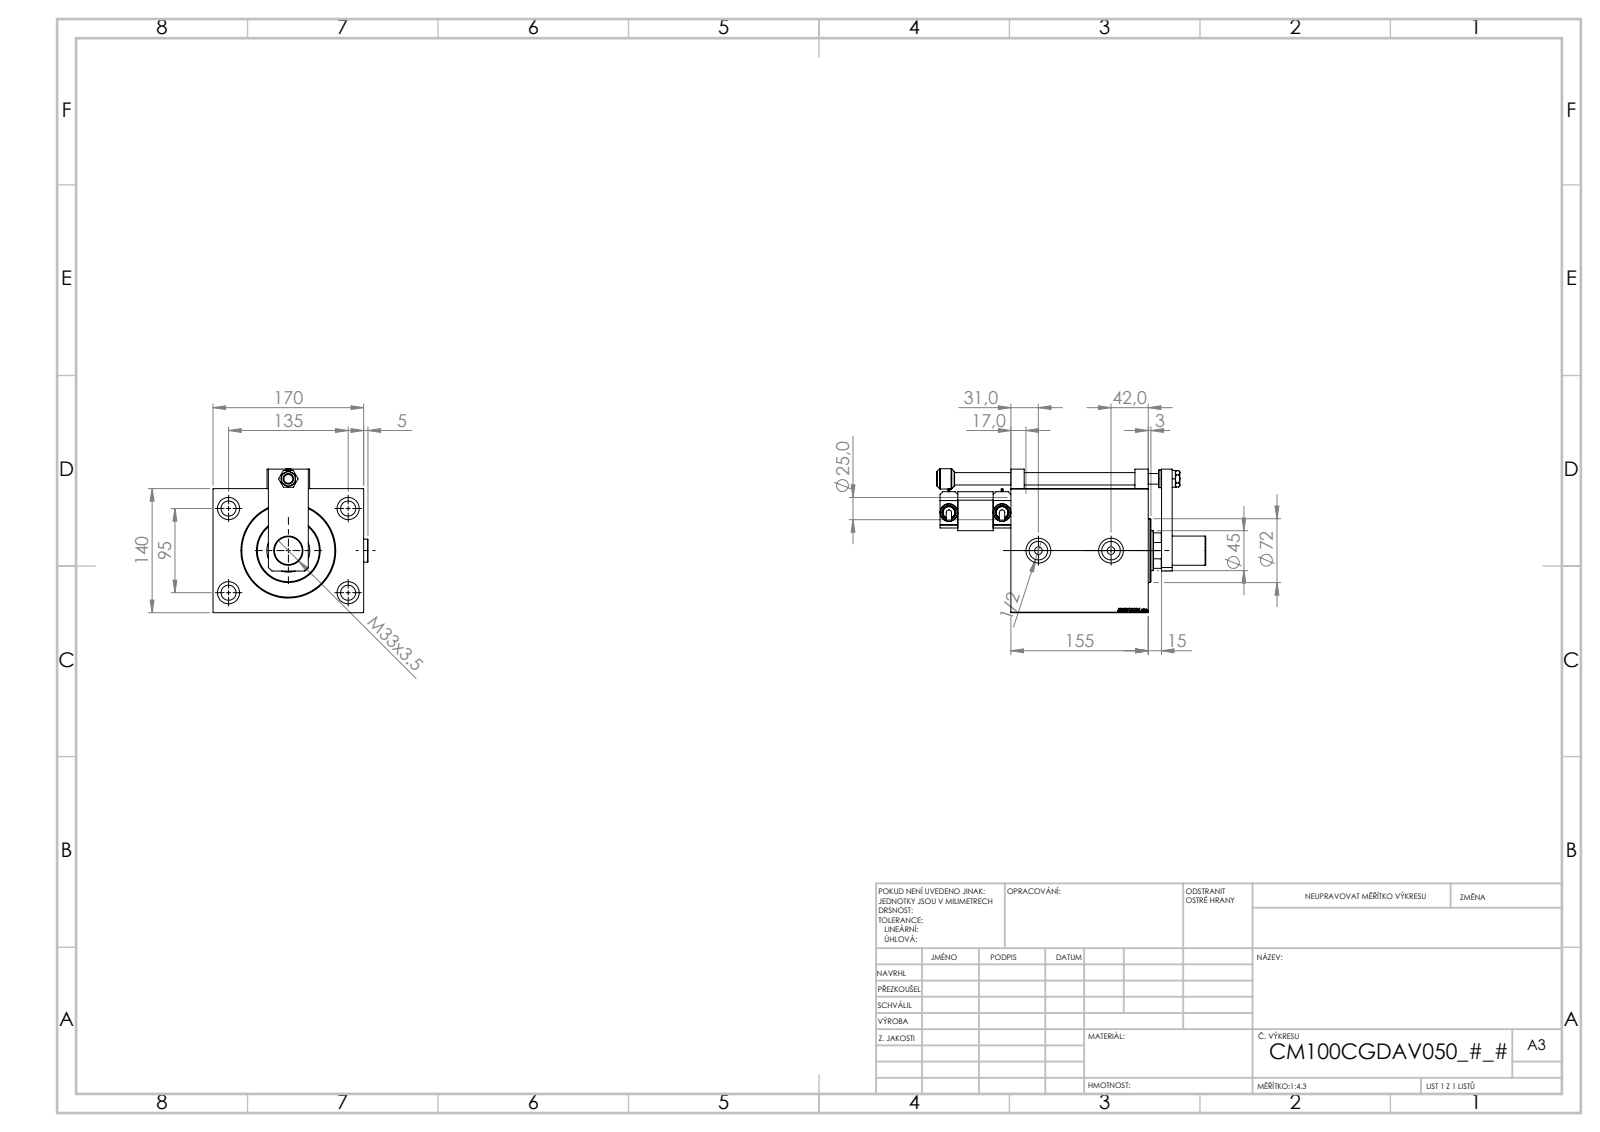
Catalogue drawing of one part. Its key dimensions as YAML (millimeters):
part_name: "TYC_P; SWITCH P; NUT_D16; NUT_D19_P (+7 more)"
step_written_by: "SolidWorks 2019 (CONFIG_CONTROL_DESIGN)"
units: millimeters
bodies: {solids: 17, faces: 1158, planar: 559, cylindrical: 140, other: 459}
overall_size: [303.6, 174.9, 162.5]
volume: 3474000
surface_area: 371654
round_holes:
  - {diameter: 4, count: 4}
  - {diameter: 8, count: 4}
  - {diameter: 17, count: 4}
  - {diameter: 25, count: 4}
  - {diameter: 8.5, count: 2}
  - {diameter: 20.96, count: 2}
  - {diameter: 28, count: 2}
  - {diameter: 12, count: 1}
  - {diameter: 13, count: 1}
  - {diameter: 14, count: 1}
  - {diameter: 31.5, count: 1}
  - {diameter: 33, count: 1}
round_bosses_or_shafts:
  - {diameter: 20, count: 3}
  - {diameter: 26, count: 2}
  - {diameter: 16, count: 2}
  - {diameter: 14, count: 2}
  - {diameter: 6, count: 2}
  - {diameter: 72, count: 1}
  - {diameter: 31, count: 1}
  - {diameter: 23, count: 1}
partial_cylinders:
  - {radius: 3, count: 1}
  - {radius: 22, count: 1}
face_to_face_distances: [140, 170, 155, 129, 26, 15, 65, 80, 114, 50]
hole_center_spacings: [82.54, 20, 75.36, 95, 135, 140, 141.42, 145.15]
